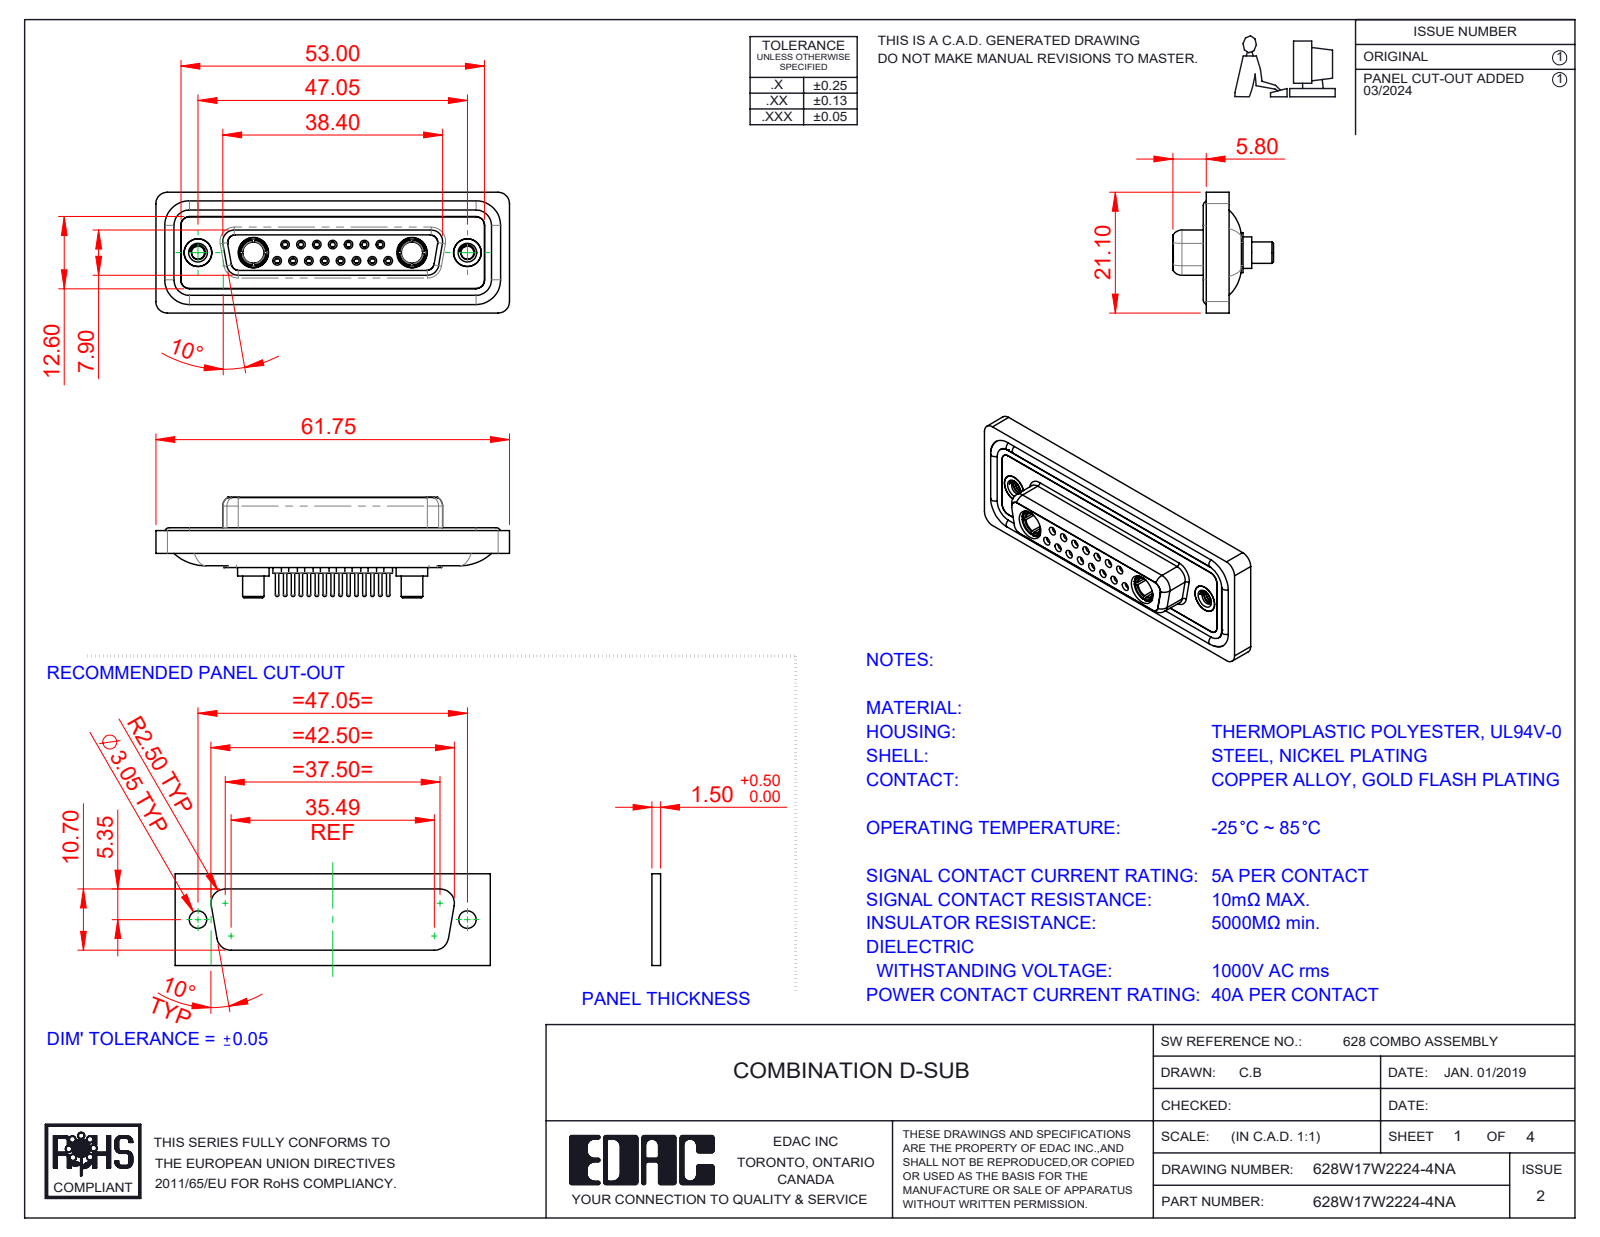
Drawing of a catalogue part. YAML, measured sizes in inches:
part_name: "628Combo Threaded Rivet_A; 628Combo Contact Row 1_24; 628Combo Shell Rear_25 Contacts; Power Socket_40A S (+5 more)"
step_written_by: "SolidWorks 2023 (CONFIG_CONTROL_DESIGN)"
units: inches
bodies: {solids: 26, faces: 1357, planar: 388, cylindrical: 521, other: 448}
overall_size: [2.431, 0.831, 0.691]
volume: 0.51
surface_area: 21.51
round_holes:
  - {diameter: 0.035, count: 15}
  - {diameter: 0.043, count: 15}
  - {diameter: 0.059, count: 15}
  - {diameter: 0.079, count: 15}
  - {diameter: 0.063, count: 8}
  - {diameter: 0.067, count: 7}
  - {diameter: 0.191, count: 4}
  - {diameter: 0.089, count: 2}
  - {diameter: 0.146, count: 2}
  - {diameter: 0.157, count: 2}
  - {diameter: 0.159, count: 2}
  - {diameter: 0.197, count: 2}
round_bosses_or_shafts:
  - {diameter: 0.087, count: 15}
  - {diameter: 0.024, count: 15}
  - {diameter: 0.063, count: 11}
  - {diameter: 0.217, count: 2}
  - {diameter: 0.205, count: 2}
  - {diameter: 0.195, count: 2}
  - {diameter: 0.195, count: 2}
  - {diameter: 0.189, count: 2}
partial_cylinders:
  - {radius: 0.059, count: 22}
  - {radius: 0.079, count: 18}
  - {radius: 0.053, count: 8}
  - {radius: 0.063, count: 8}
  - {radius: 0.01, count: 4}
  - {radius: 0.02, count: 4}
  - {radius: 0.024, count: 4}
  - {radius: 0.026, count: 4}
face_to_face_distances: [0.016, 0.071, 0.293, 0.222, 0.26, 0.02, 0.278, 0.063, 0.114, 0.043]
hole_center_spacings: [0.124, 0.109, 0.327, 0.218, 0.198, 0.198, 0.295, 0.436]
